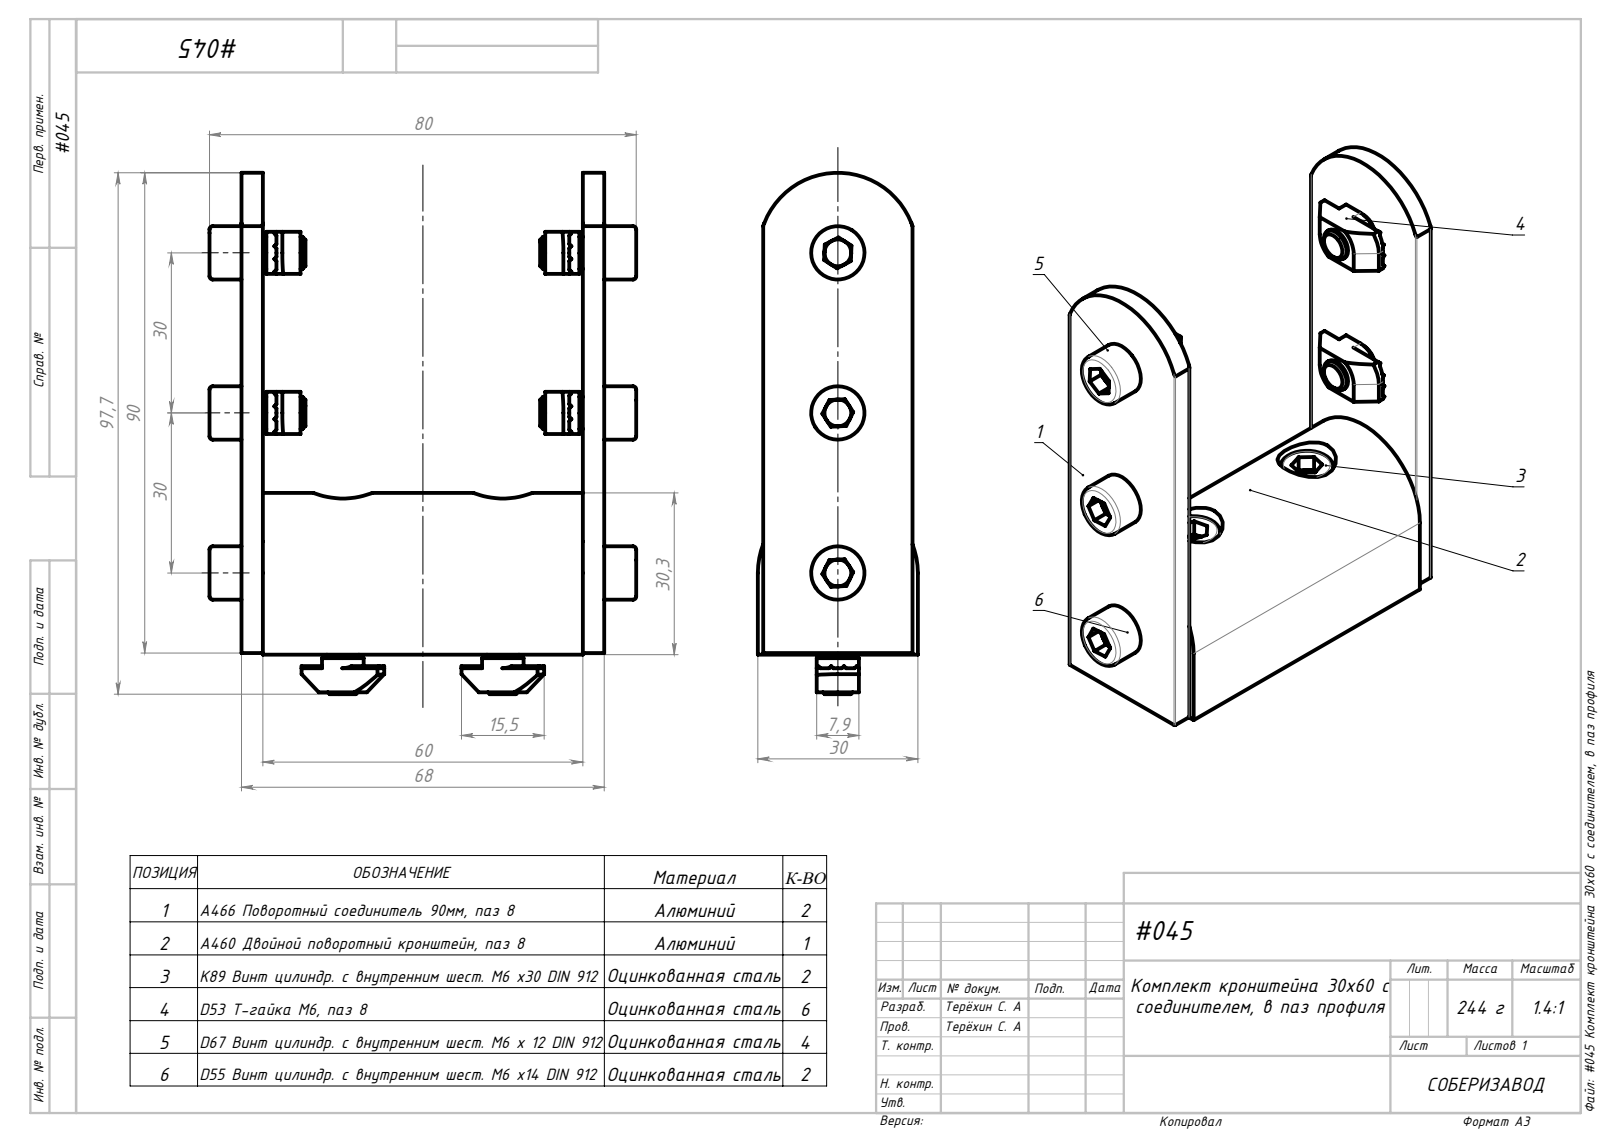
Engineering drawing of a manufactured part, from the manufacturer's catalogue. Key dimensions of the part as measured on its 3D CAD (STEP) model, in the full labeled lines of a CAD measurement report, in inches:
Part name (STEP PRODUCT): A466 Поворотный соединитель 90мм, паз 8; #045 Комплект кронштейна 30х60 с соединителем, в паз профиля; A460 Двойной поворотный кронштейн, паз 8; D53 Т-гайка М6, паз 8_00 (+3 more)
STEP written by: SolidWorks 2021 (AUTOMOTIVE_DESIGN)
Units: inches
Bodies: 17 solids, 550 faces (329 planar, 105 cylindrical, 116 other)
Overall size (bounding box): 3.846 × 3.15 × 1.181
Volume: 4.471 in³ · Surface area: 46.88 in²
Round holes (diameter × count): ⌀0.197 ×4, ⌀0.252 ×3, ⌀0.242 ×2, ⌀0.433 ×2, ⌀0.203 ×1
Round bosses / shafts (diameter × count): ⌀0.394 ×5, ⌀0.236 ×5
Partial cylindrical surfaces — rounded edges, fillets, slot ends (radius × count): R0.157 ×12, R0.008 ×8, R0.27 ×8, R0.583 ×1, R0.591 ×1
Main face-to-face distances: 0.157, 2.52, 2.362, 2.677, 1.181, 0.039, 1.142, 1.102, 0.435, 0.311
Hole centre spacings: 1.181, 2.362
